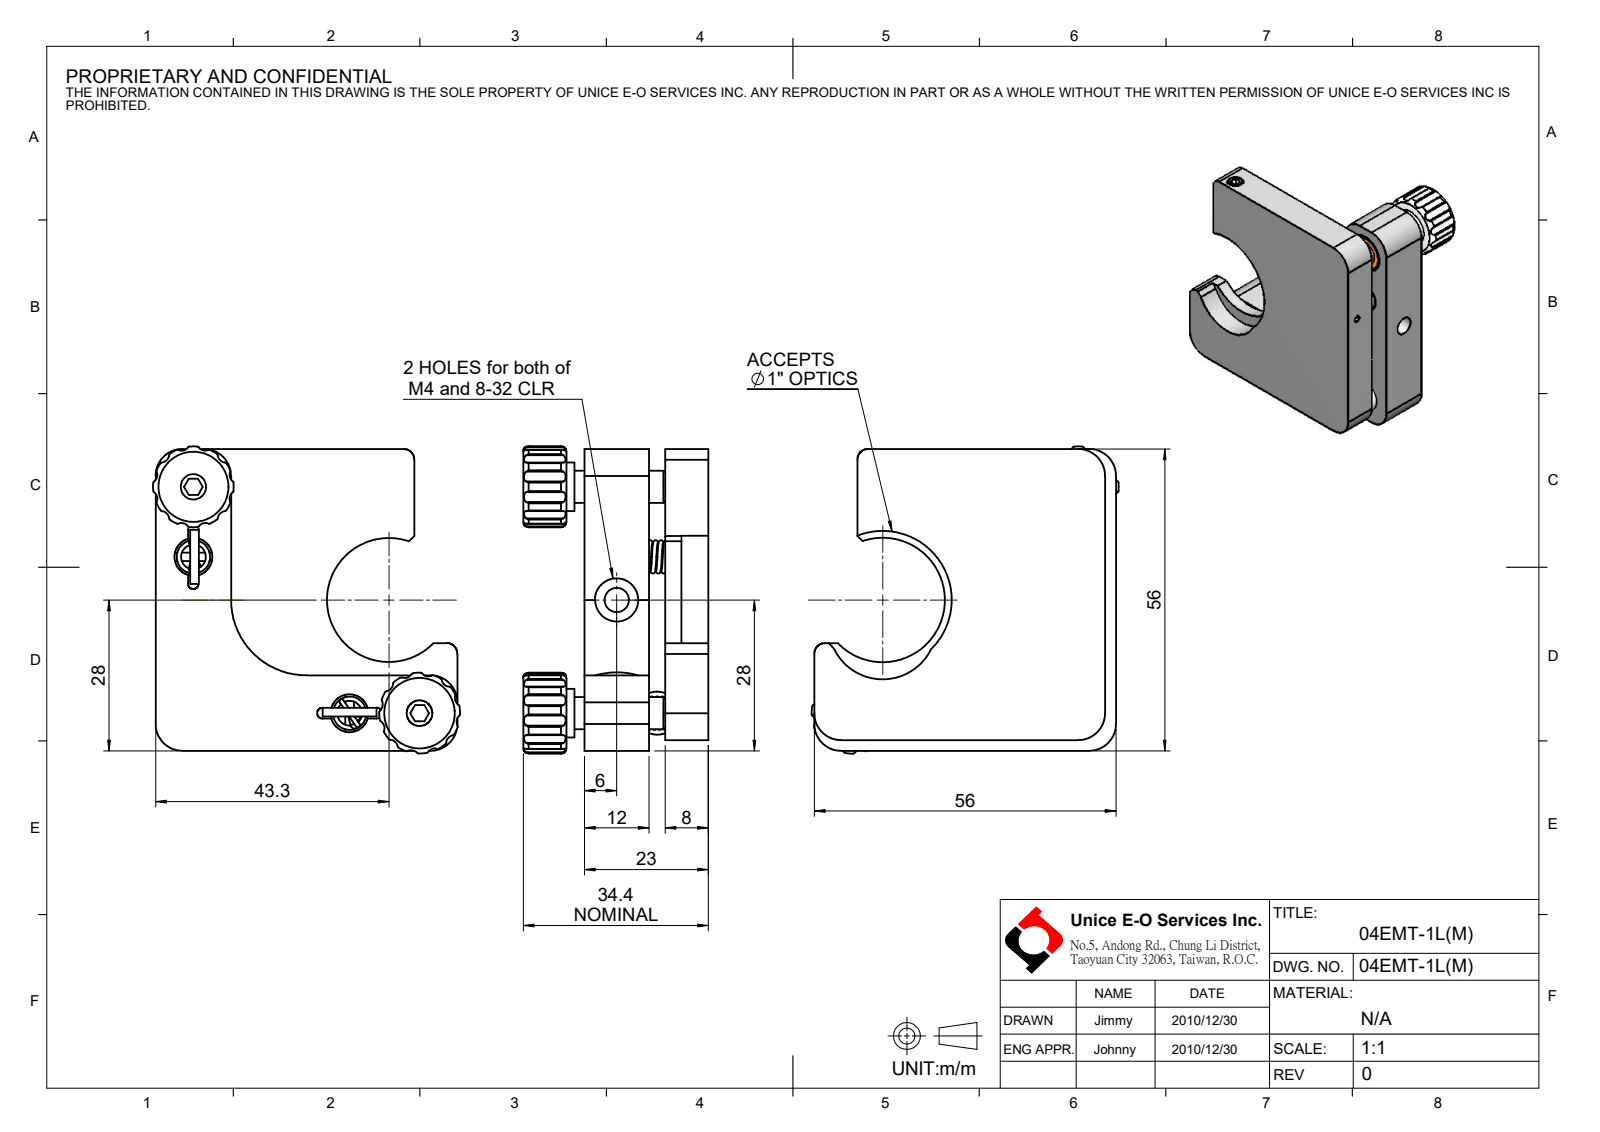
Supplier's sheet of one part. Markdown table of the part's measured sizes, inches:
| quantity | value |
| --- | --- |
| part name | 04EMT-1L(M) |
| STEP written by | SolidWorks 2016 (CONFIG_CONTROL_DESIGN) |
| units | inches |
| bodies | 22 solids, 424 faces (115 planar, 230 cylindrical, 79 other) |
| overall size | 2.244 × 2.244 × 1.358 |
| volume | 2.154 in³ |
| surface area | 30.52 in² |
| round holes (diameter × count) | 0.047 × 4, 0.067 × 2, 0.157 × 2, 0.177 × 2, 0.185 × 2, 0.232 × 2, 0.236 × 2, 0.276 × 2, 0.315 × 2, 0.374 × 2, 0.059 × 1, 0.13 × 1 |
| round bosses / shafts (diameter × count) | 0.063 × 5, 0.354 × 2, 0.059 × 2, 0.031 × 2, 0.157 × 1 |
| partial cylindrical surfaces (radius × count) | 0.012 × 48, 0.059 × 25, 0.197 × 8, 0.03 × 4, 0.039 × 4, 0.079 × 2, 0.295 × 2, 0.394 × 1 |
| main face-to-face distances | 0.315, 0.472, 0.118, 0.591, 0.906, 0.433, 0.079, 0.551, 2.205, 2.126 |
| hole center spacings | 0.512, 0.635, 0.836, 1.343, 2.009, 0.287, 0.822, 1.597 |
